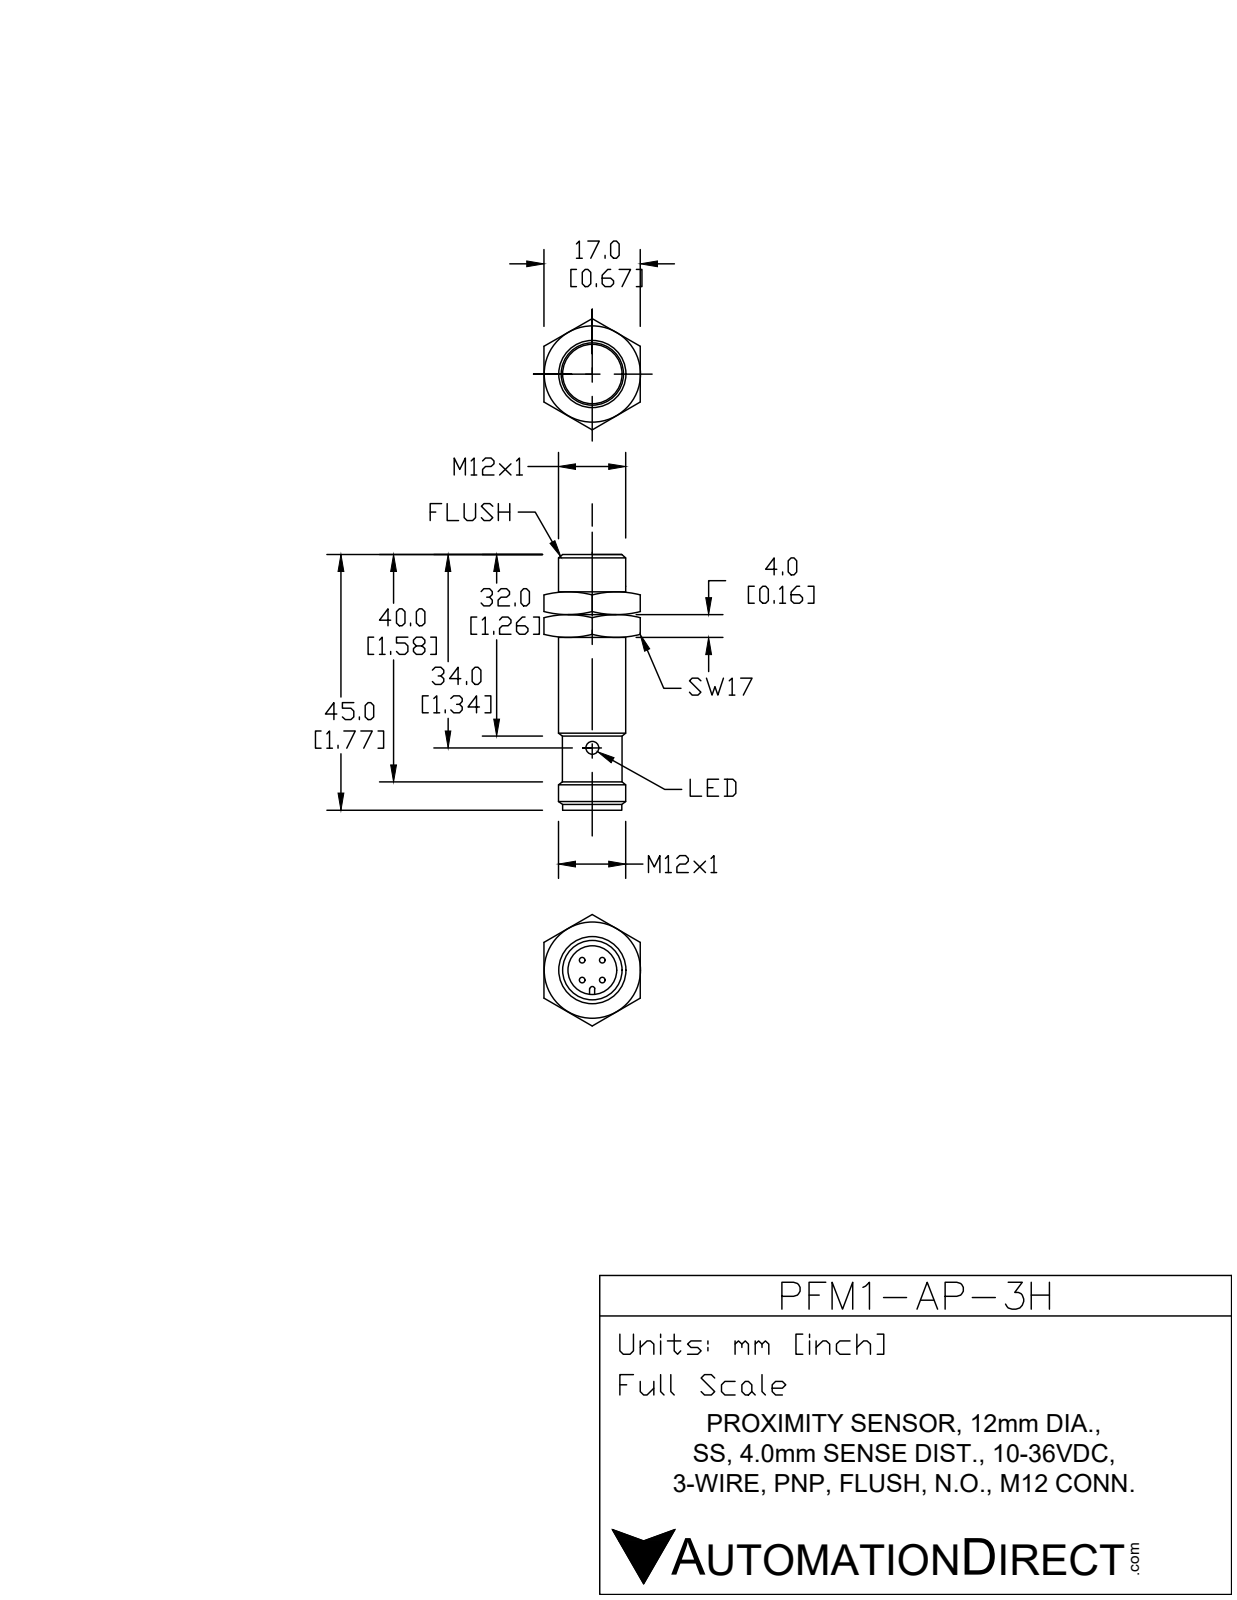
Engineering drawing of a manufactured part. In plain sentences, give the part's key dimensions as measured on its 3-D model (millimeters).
The part is named "PFM1-AP-3H". Its 3-D file was written by "SolidWorks 2017 (AUTOMOTIVE_DESIGN)". It is 3 solids with 101 faces: 29 planar, 27 cylindrical and 45 other. Overall it measures 45.3 by 19.6 by 17 millimeters. Its volume is 5 570 cubic millimeters and its surface area 3 452 square millimeters. Round holes: 2 of diameter 2.5, 1 of diameter 3, 1 of diameter 8.4, 1 of diameter 10.9. Round bosses or shafts: 1 of diameter 12, 1 of diameter 10.6, 1 of diameter 10.5, 1 of diameter 10.3. Partial cylindrical surfaces (rounded edges, fillets, slot ends): 1 of radius 0.6. The main face-to-face distances are 4, 17, 8, 15.3, 11.3, 7.3, 21.1, 25.1, 29.1, 36.4.
